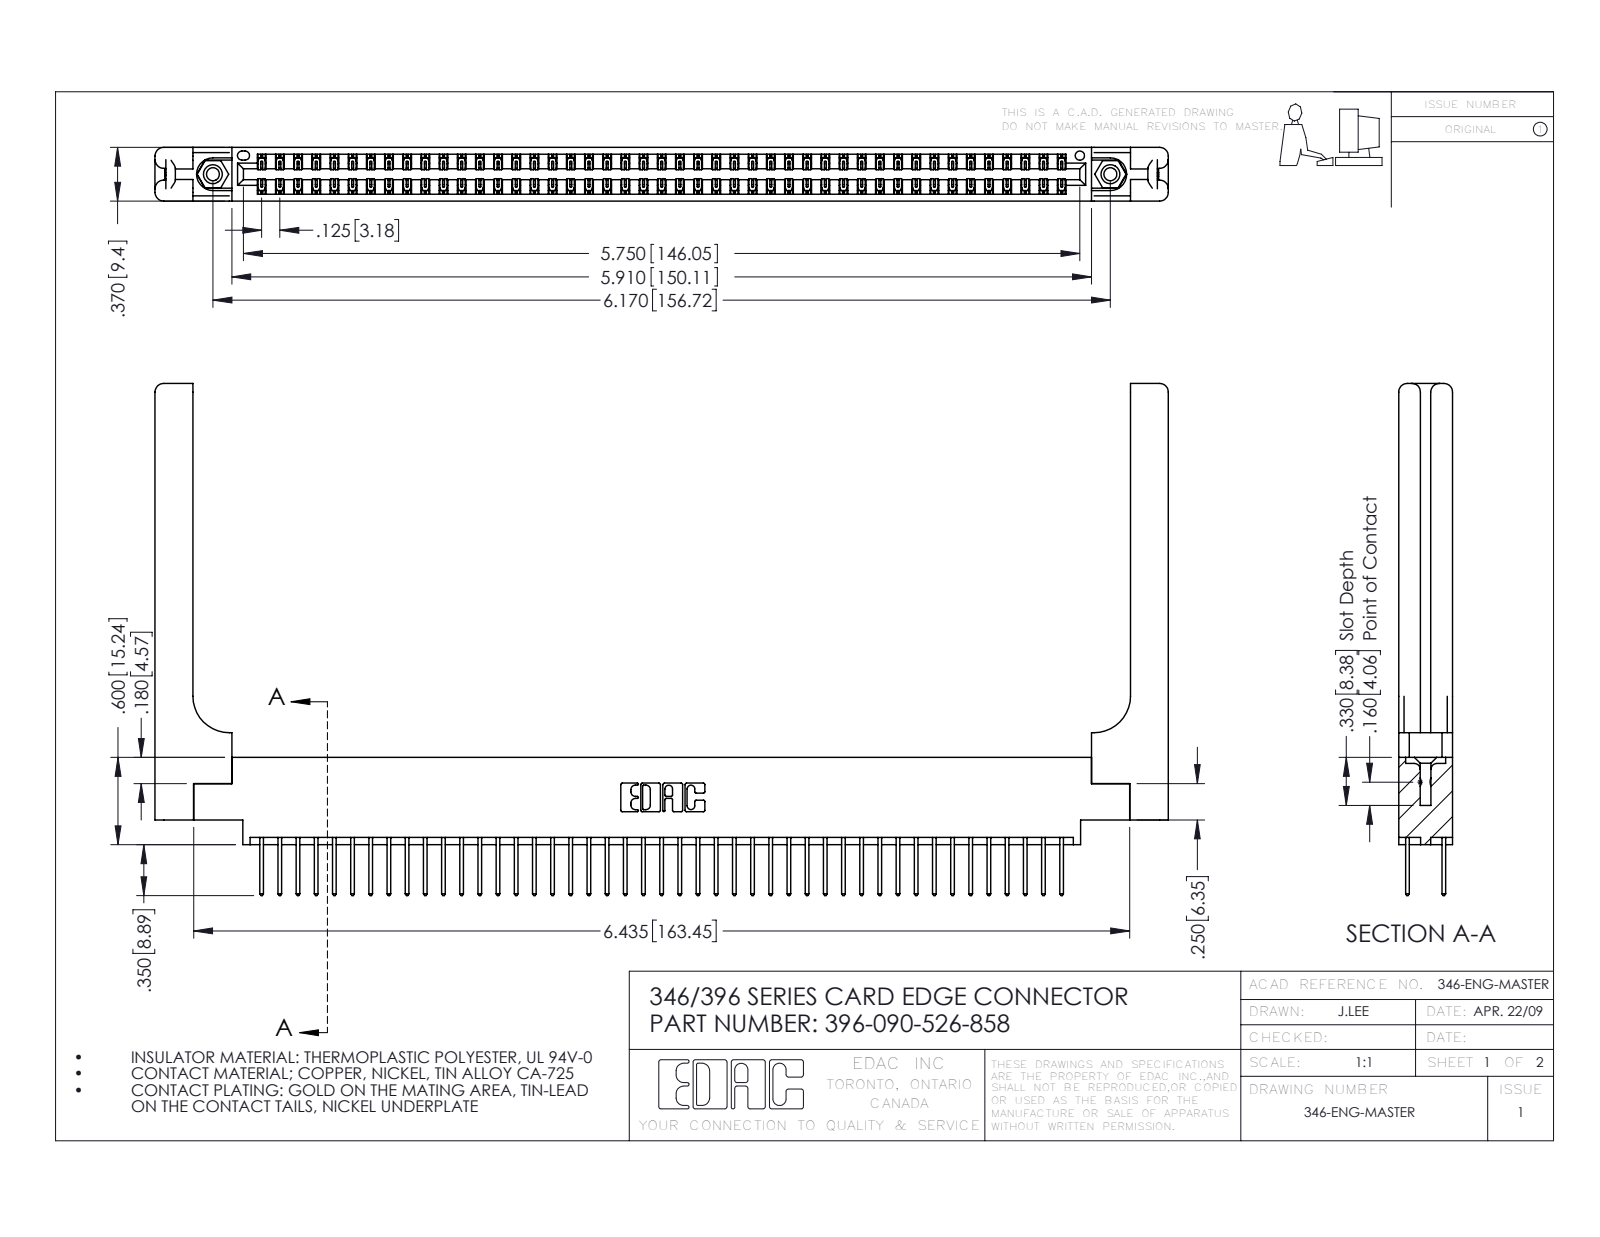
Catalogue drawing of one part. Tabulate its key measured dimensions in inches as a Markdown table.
| quantity | value |
| --- | --- |
| part name | 346-220-058_345-220-058; 345-250-001_345-250-001-102; 345-292-001_345-293-126; 396-090-526-858 (+1 more) |
| STEP written by | SolidWorks 2016 (CONFIG_CONTROL_DESIGN) |
| units | inches |
| bodies | 95 solids, 5062 faces (3378 planar, 1624 cylindrical, 60 other) |
| overall size | 6.966 × 3.52 × 0.37 |
| volume | 1.511 in³ |
| surface area | 45.88 in² |
| round holes (diameter × count) | 0.089 × 2, 0.125 × 2, 0.156 × 2, 0.064 × 1 |
| round bosses / shafts (diameter × count) | 0.155 × 2 |
| partial cylindrical surfaces (radius × count) | 0.006 × 135, 0.01 × 90, 0.01 × 22, 0.06 × 16, 0.007 × 6, 0.031 × 6, 0.026 × 3, 0.014 × 2 |
| main face-to-face distances | 0.048, 0.322, 0.37, 0.072, 0.25, 0.025, 0.298, 0.148, 0.15, 0.275 |
| hole center spacings | 0.246, 5.961, 6.17 |
